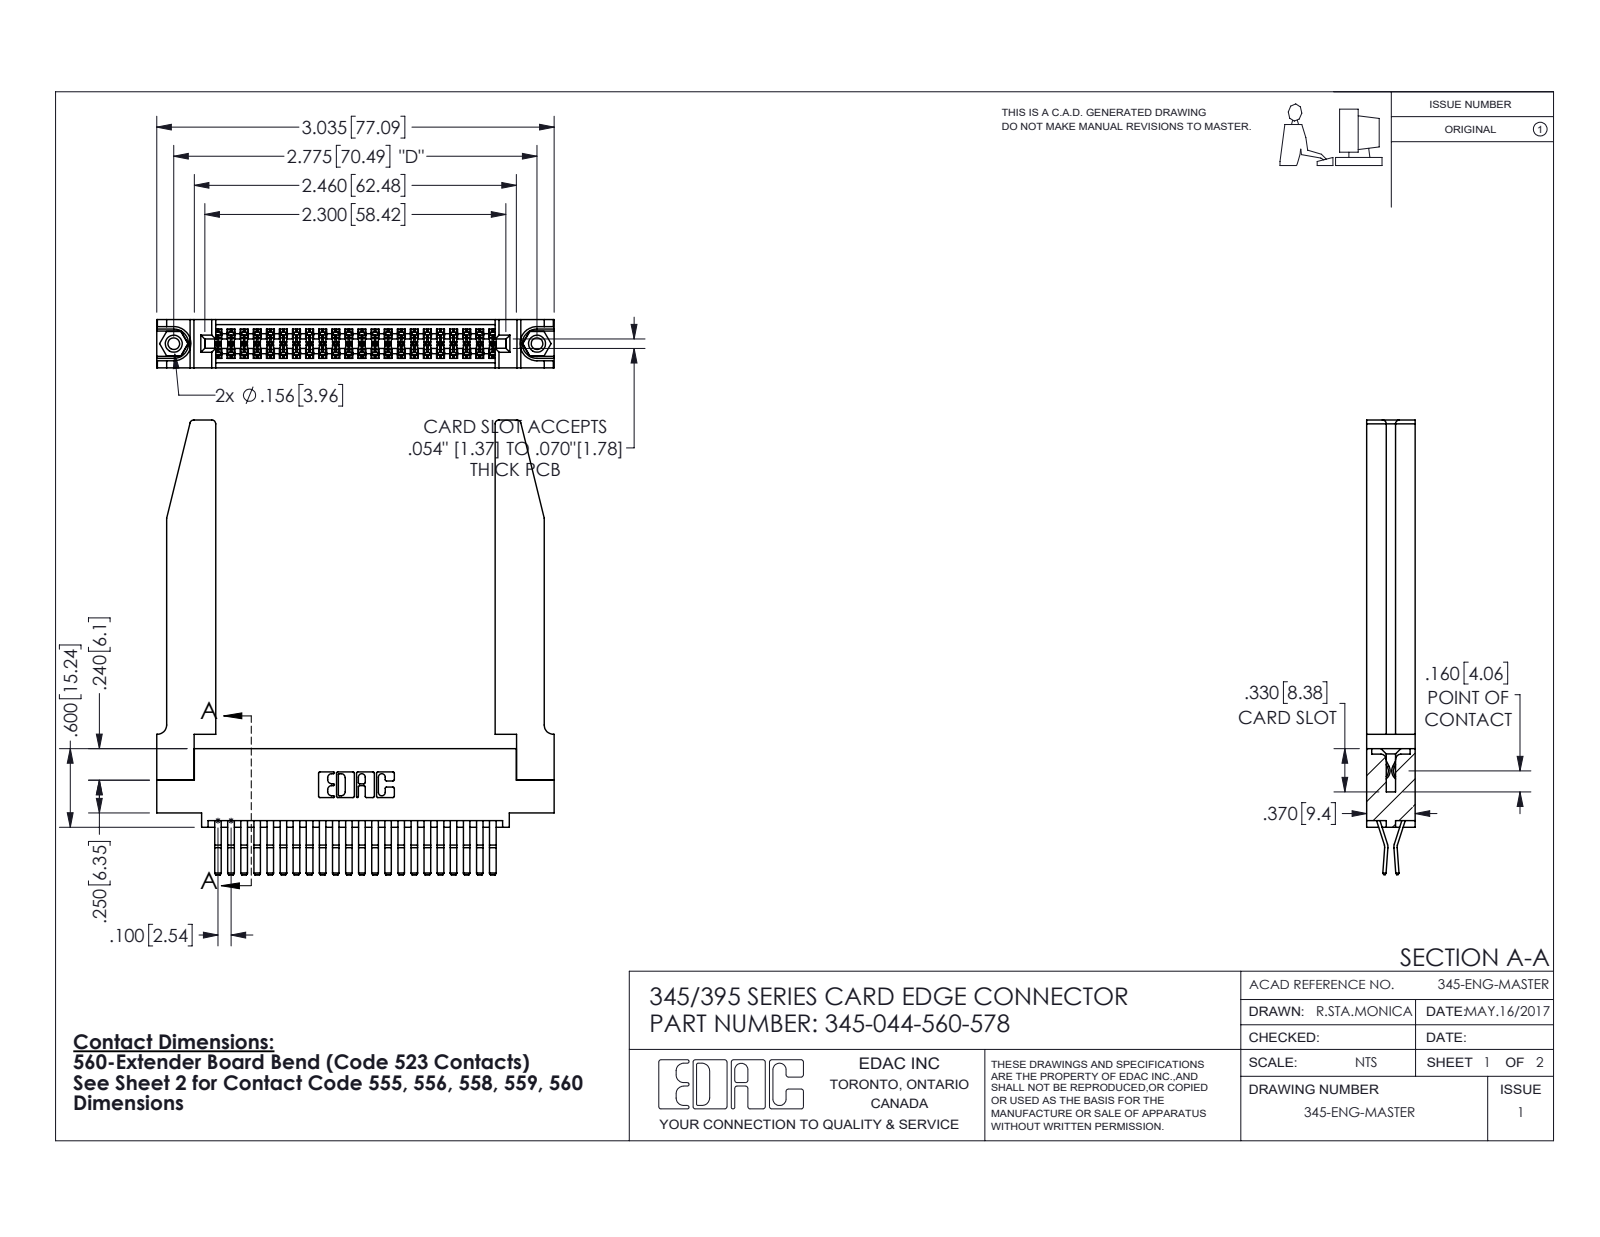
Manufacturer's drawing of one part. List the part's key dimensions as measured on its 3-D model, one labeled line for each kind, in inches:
Part name (STEP PRODUCT): 345-292-001_560 Tail; 345-220-078_345-220-078; 345 Part_0.110 Offset - 0.156 Dia-TH; 345-044-560-578 (+1 more)
STEP written by: SolidWorks 2016 (CONFIG_CONTROL_DESIGN)
Units: inches
Bodies: 49 solids, 2652 faces (1678 planar, 922 cylindrical, 52 other)
Overall size (bounding box): 3.472 × 3.036 × 0.37
Volume: 0.933 in³ · Surface area: 28.52 in²
Round holes (diameter × count): ⌀0.089 ×2, ⌀0.125 ×2, ⌀0.156 ×2, ⌀0.064 ×1
Round bosses / shafts (diameter × count): ⌀0.155 ×2
Partial cylindrical surfaces — rounded edges, fillets, slot ends (radius × count): R0.006 ×66, R0.01 ×22, R0.03 ×8, R0.007 ×6, R0.031 ×6, R0.026 ×3, R0.01 ×2, R0.014 ×2
Main face-to-face distances: 0.37, 0.072, 0.298, 0.025, 0.2, 0.098, 0.272, 0.225, 0.148, 0.15
Hole centre spacings: 0.27, 2.541, 2.775
